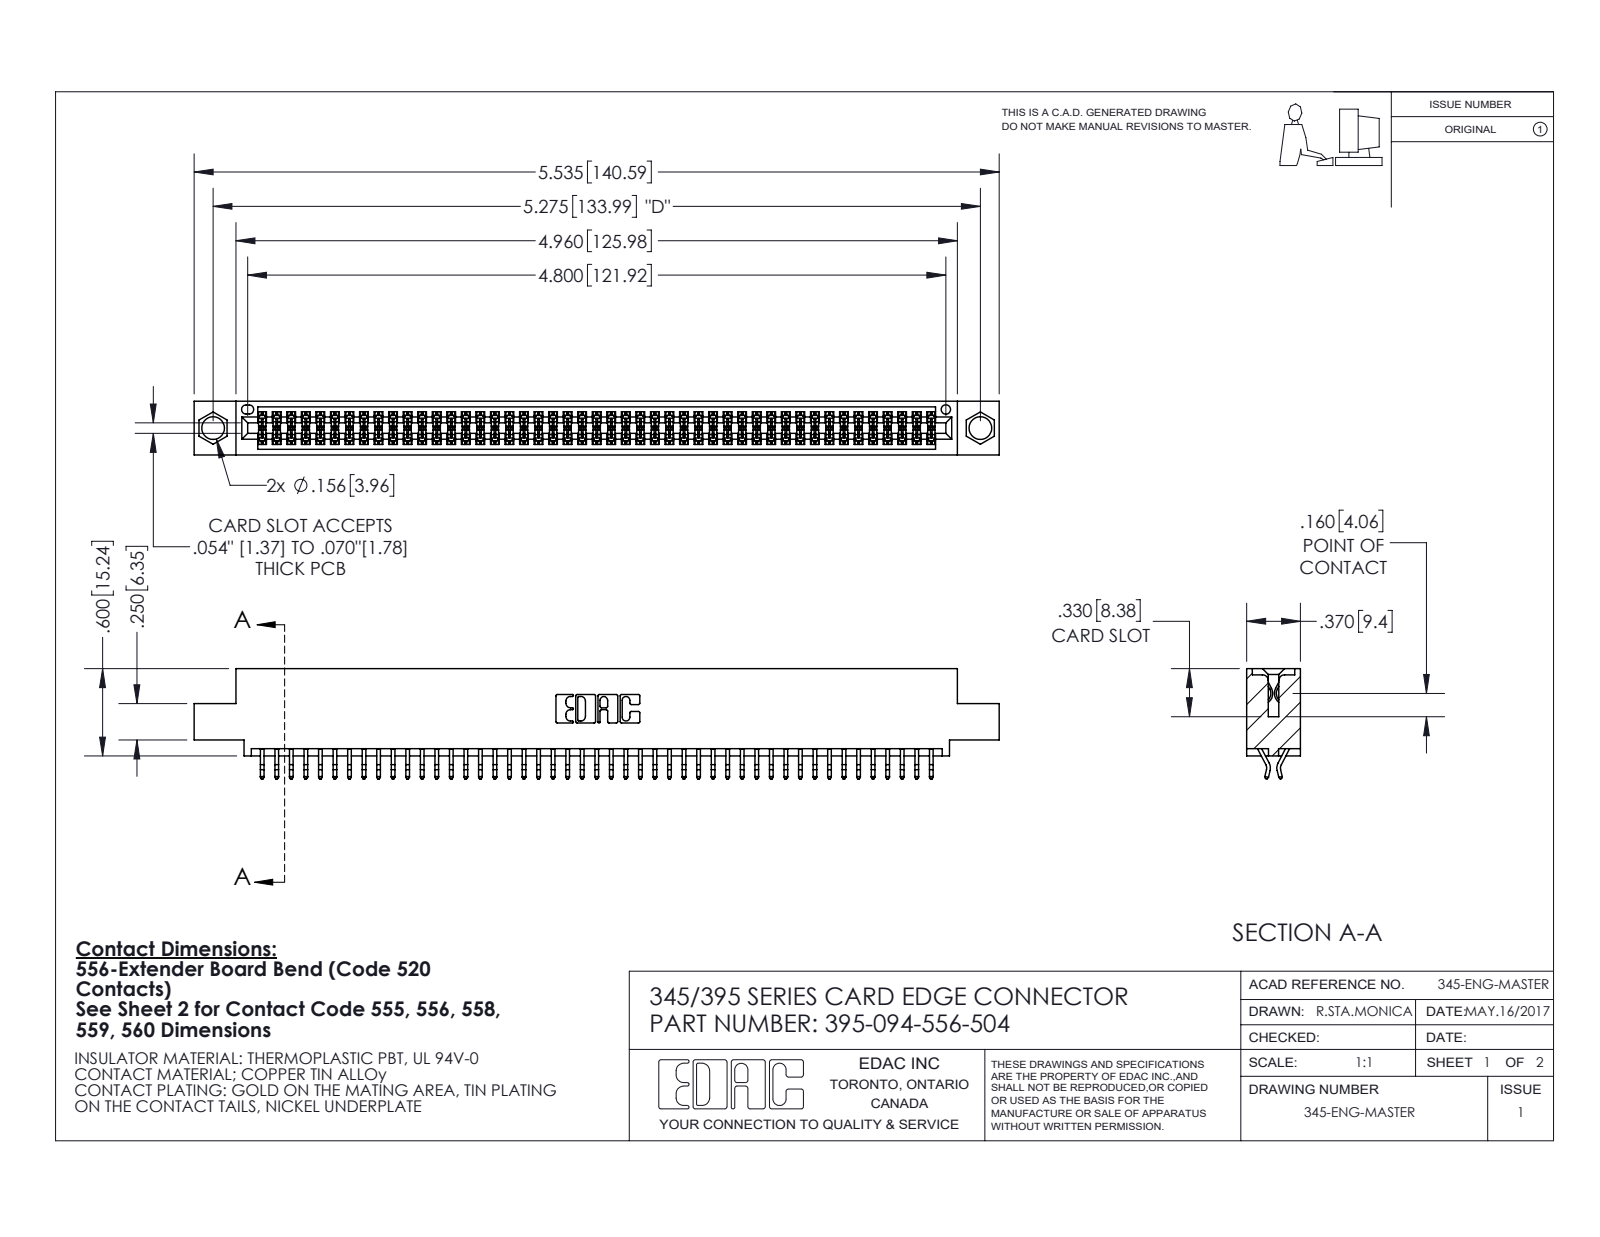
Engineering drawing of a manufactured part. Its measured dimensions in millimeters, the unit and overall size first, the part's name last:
Units: millimetres
Overall size (bounding box): 140.6 × 19.2 × 9.4
Round holes (diameter × count): ⌀4 ×2, ⌀1.6 ×1
Partial cylindrical surfaces — rounded edges, fillets, slot ends (radius × count): R0.2 ×188, R0.3 ×22, R0.2 ×6, R0.8 ×6, R0.7 ×3, R0.3 ×2, R0.4 ×2, R0.5 ×2
Main face-to-face distances: 7.6, 1.8, 9.4, 5.1, 0.6, 2.5, 6.9, 5.7, 4.4, 3.8
Hole centre spacings: 6.9, 128, 134
Volume: 13 500 mm³ · Surface area: 19 940 mm²
Bodies: 95 solids, 5408 faces (3576 planar, 1832 cylindrical, 0 other)
Part name (STEP PRODUCT): 345 Part_0.110 Offset - 0.156 Dia-TI; 345-292-001_556 Tail; 395-094-556-504
STEP written by: SolidWorks 2020 (CONFIG_CONTROL_DESIGN)
